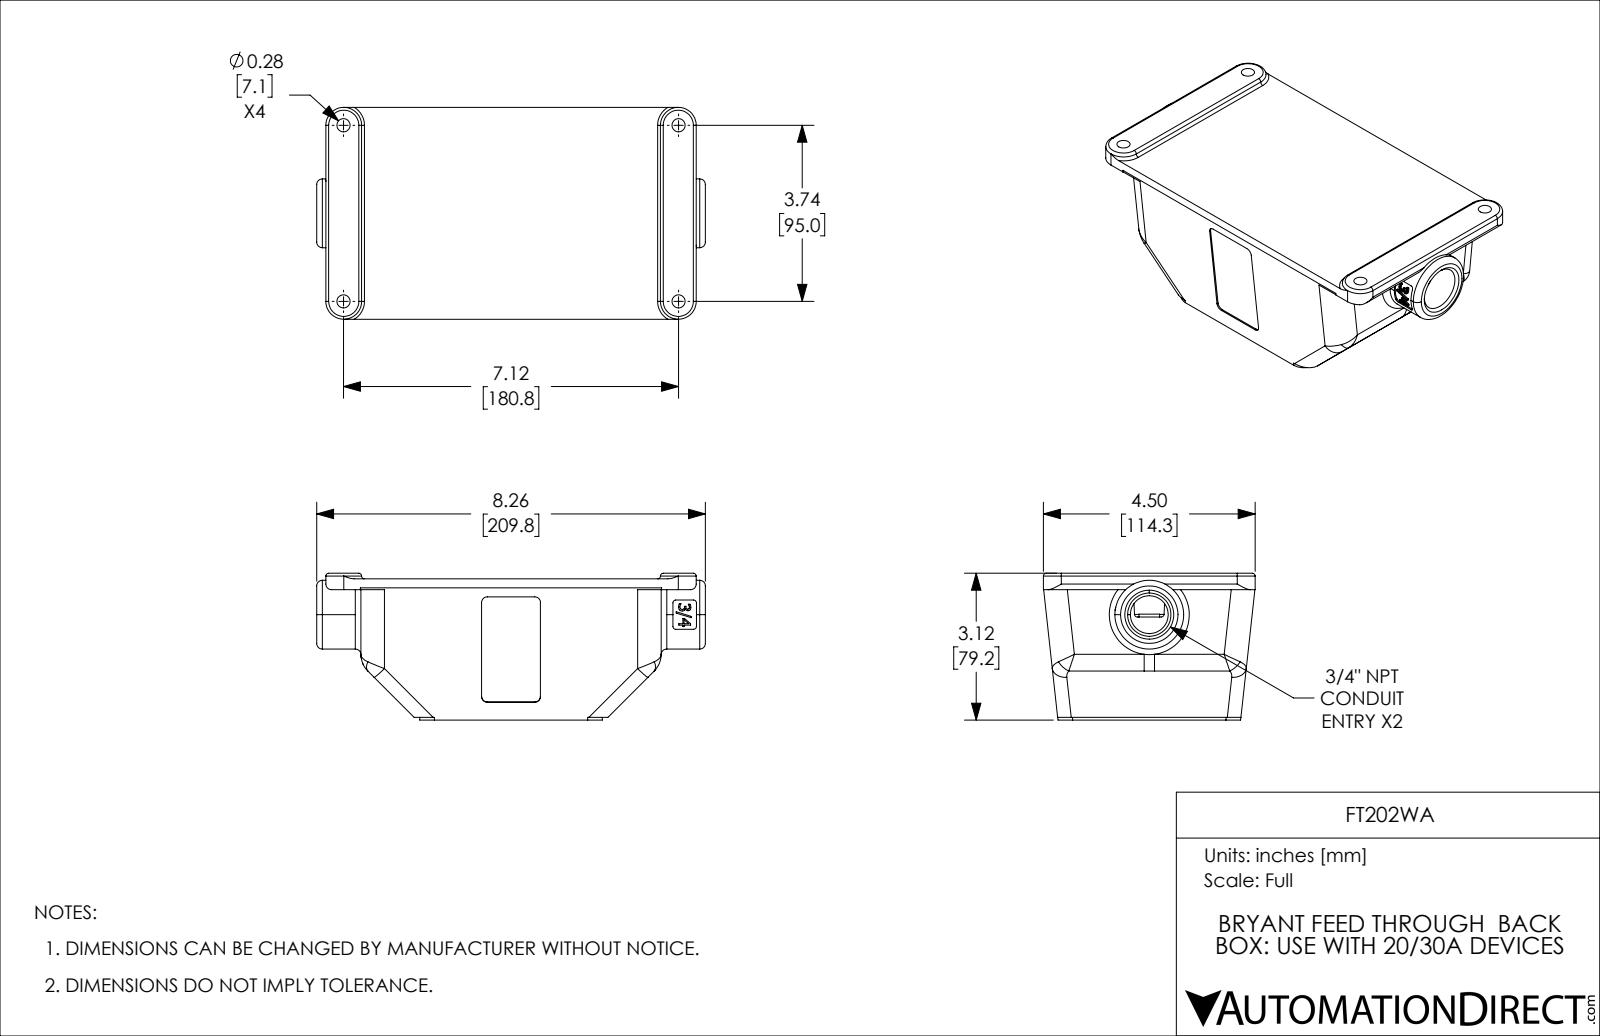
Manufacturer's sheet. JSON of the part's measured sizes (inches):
{"part_name": "FT202WA", "step_written_by": "SolidWorks 2021 (CONFIG_CONTROL_DESIGN)", "units": "inches", "bodies": {"solids": 1, "faces": 489, "planar": 108, "cylindrical": 238, "other": 143}, "overall_size": [8.26, 4.5, 3.12], "volume_in3": 21.51, "surface_area_in2": 209.3, "round_holes": [[0.145, 4], [0.28, 4], [0.13, 1], [0.803, 1], [0.92, 1], [1.12, 1]], "round_bosses_or_shafts": [[1.46, 1]], "partial_cylinders_radius": [[0.06, 38], [0.09, 12], [0.12, 10], [0.31, 10], [0.5, 6], [0.19, 4], [0.254, 4], [0.38, 4]], "face_to_face_distances": [0.19, 0.19, 3, 2.81, 6.19, 0.12, 0.31, 3.12, 6, 0.23], "hole_center_spacings": [2.021, 3.125, 3.971, 5.131, 6.166, 1.651, 3.027, 3.146]}
